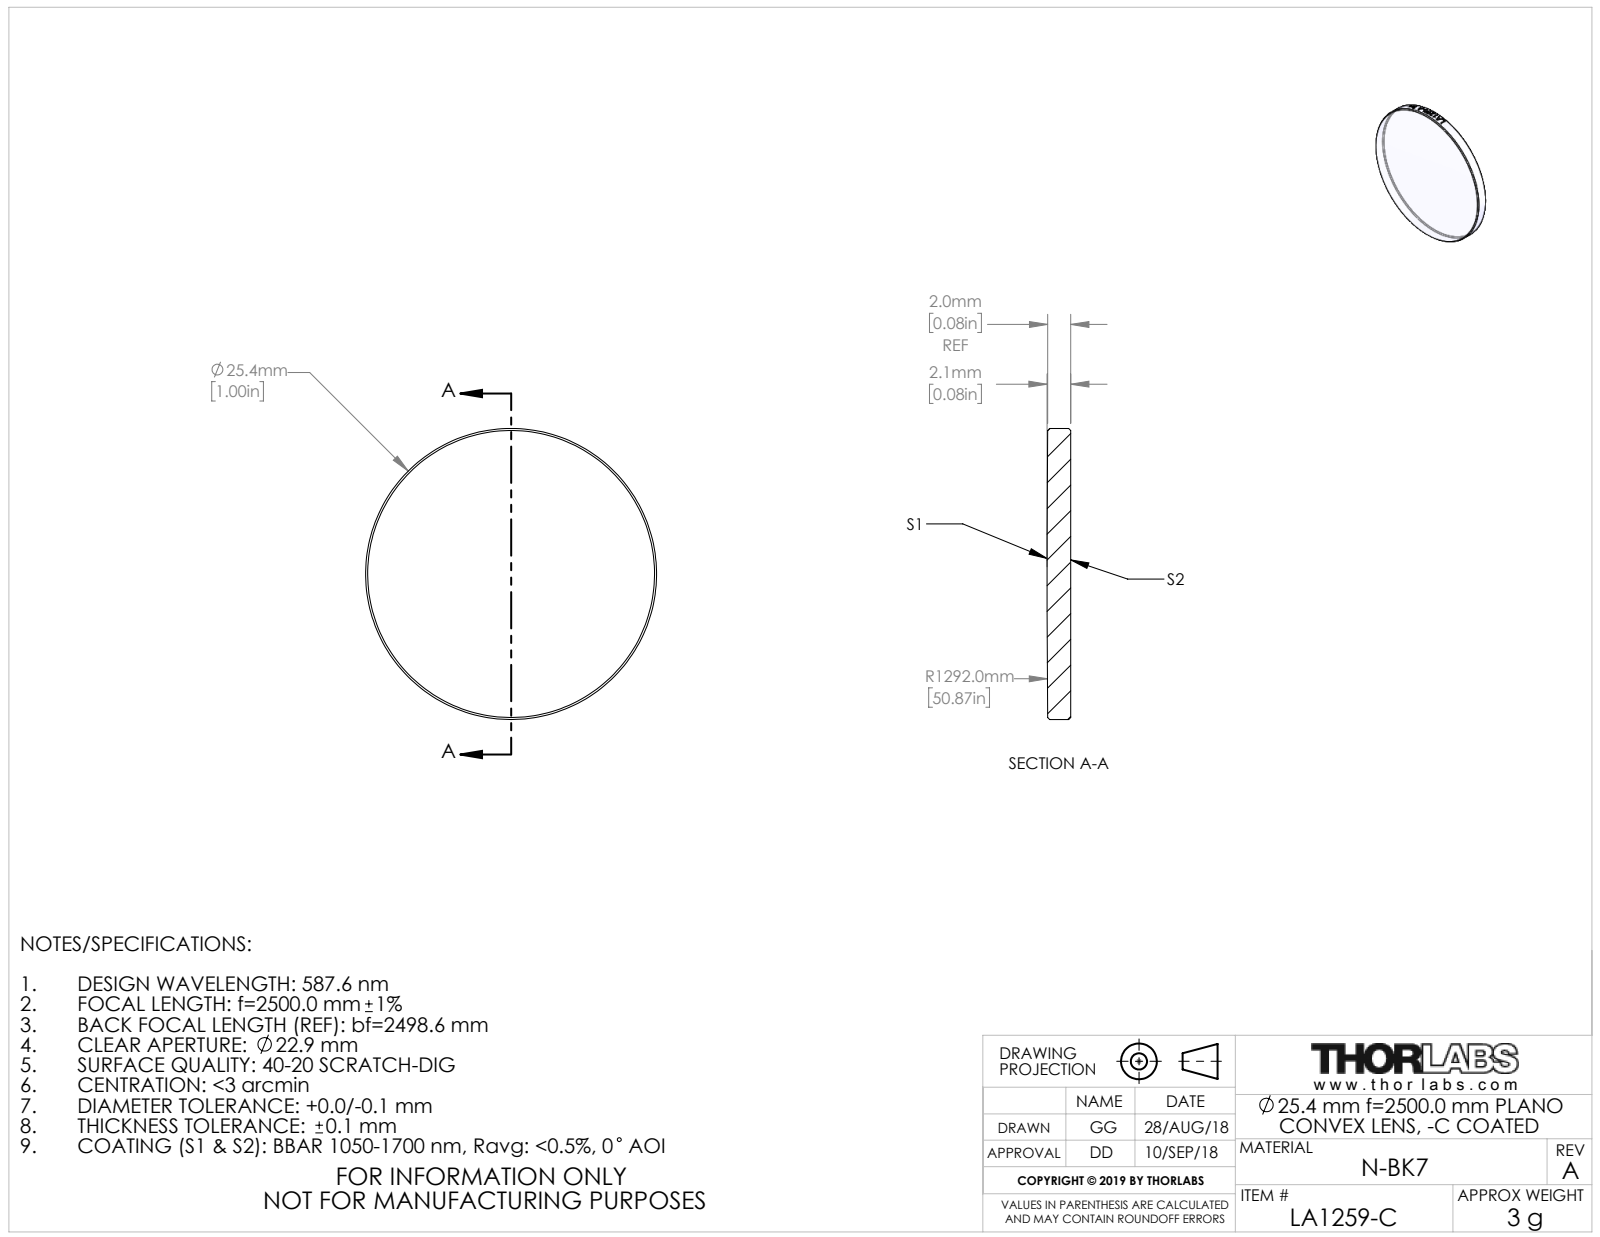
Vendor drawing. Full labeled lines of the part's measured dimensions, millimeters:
Part name (STEP PRODUCT): TTN162133-E0W
STEP written by: SolidWorks 2018 (CONFIG_CONTROL_DESIGN)
Units: millimetres
Bodies: 1 solid, 24 faces (1 planar, 17 cylindrical, 6 other)
Overall size (bounding box): 25.4 × 25.4 × 2.06
Volume: 1 026 mm³ · Surface area: 1 156 mm²
Round bosses / shafts (diameter × count): ⌀25.4 ×1
